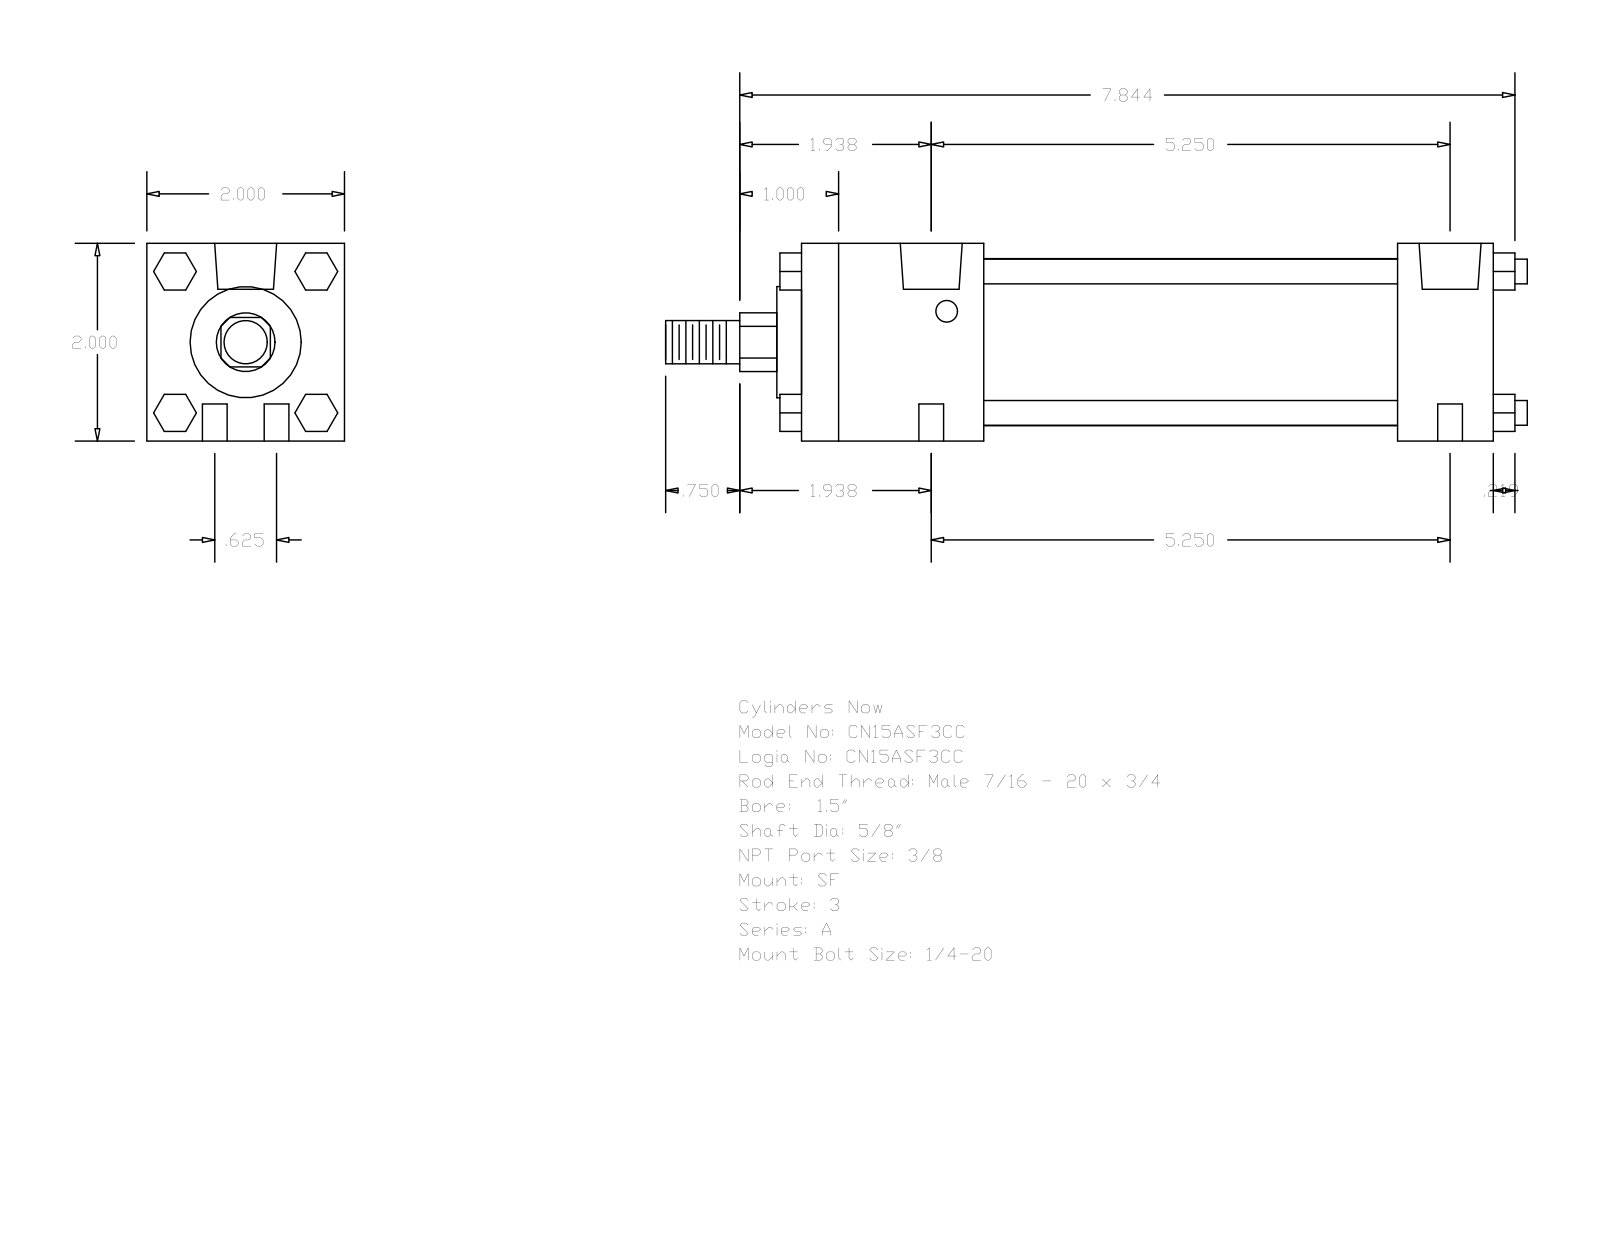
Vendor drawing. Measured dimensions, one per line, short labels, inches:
name: A_SF__0150_0.625
written by: GSSL Pune (CONFIG_CONTROL_DESIGN)
unit: in
bodies: 0 solids, 124 faces (94 planar, 30 cylindrical, 0 other)
size: 8.719 × 2 × 2
holes: 4× ⌀0.25, 2× ⌀0.219, 2× ⌀0.627
bosses: 4× ⌀0.25, 1× ⌀1.69, 1× ⌀1.125, 1× ⌀0.625, 1× ⌀0.437
rounds: 1× R0.297
face distances: 2, 7, 1.844, 6.031, 4.187, 5.156, 0.969, 0.25, 0.375, 2.094
hole spacings: 0.313, 5.259, 5.25, 0.625, 5.287, 4.937
